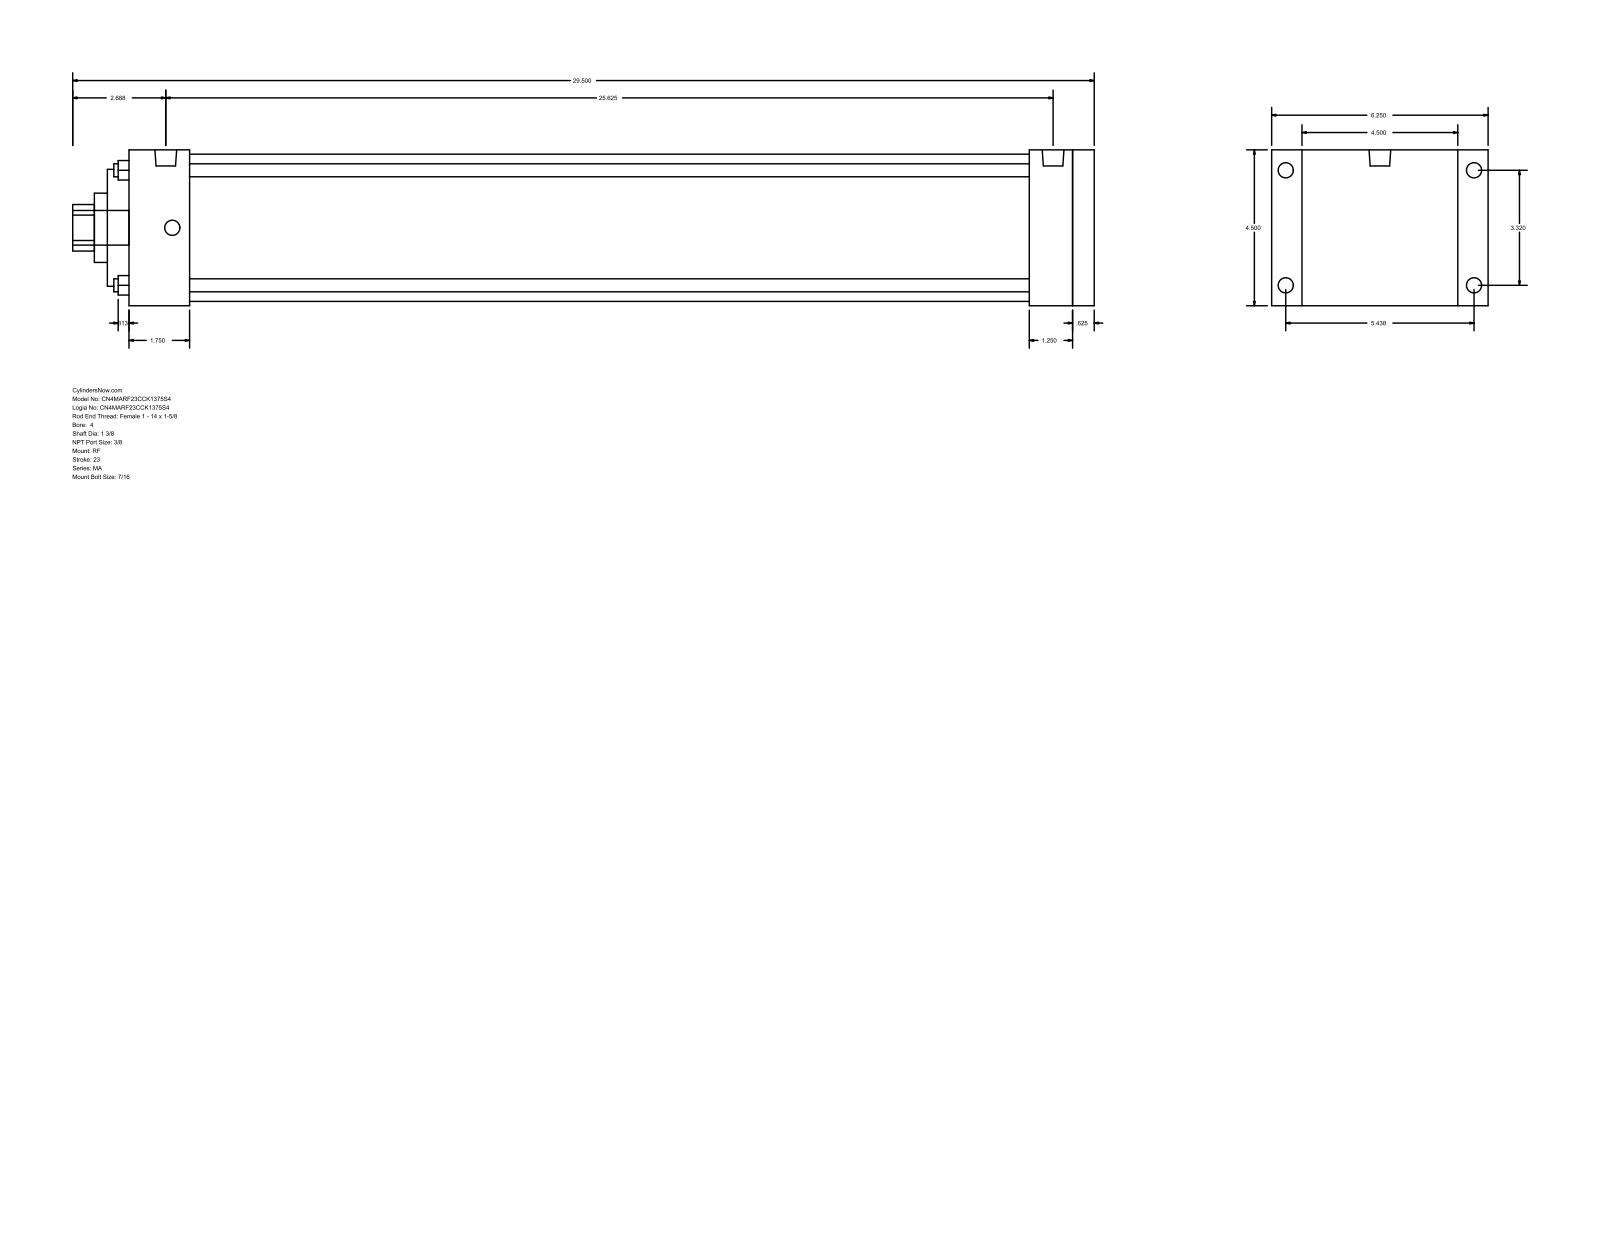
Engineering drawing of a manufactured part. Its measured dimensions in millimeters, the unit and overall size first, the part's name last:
Units: millimetres
Overall size (bounding box): 749.3 × 158.75 × 114.3
Round holes (diameter × count): ⌀9.53 ×4, ⌀34.92 ×1, ⌀50.8 ×1, ⌀85.72 ×1, ⌀107.95 ×1
Round bosses / shafts (diameter × count): ⌀11.11 ×8, ⌀15.93 ×2, ⌀25.4 ×1
Partial cylindrical surfaces — rounded edges, fillets, slot ends (radius × count): R17.06 ×1
Main face-to-face distances: 114.3, 708.03, 15.88, 692.15, 15.87, 708.02, 723.9, 22.23, 136.53, 676.27
Hole centre spacings: 59.62, 84.32, 119.25
Bodies: 0 solids, 94 faces (65 planar, 29 cylindrical, 0 other)
Part name (STEP PRODUCT): MA_RF__0400_1.375
STEP written by: GSSL Pune (CONFIG_CONTROL_DESIGN)
